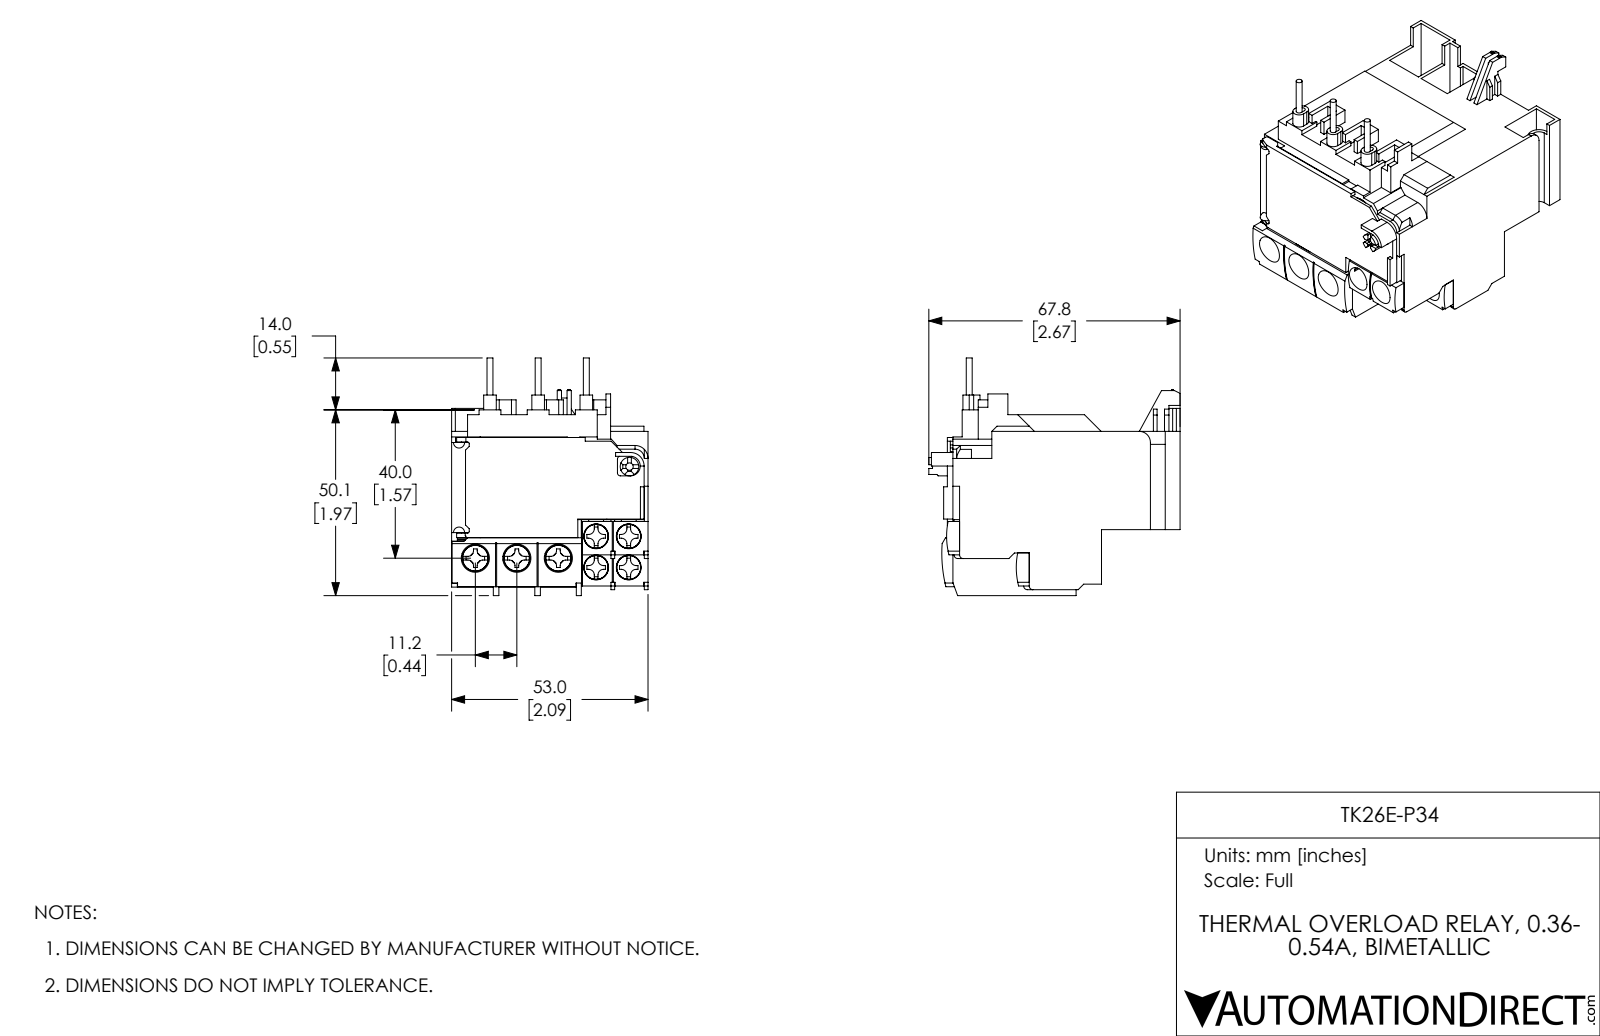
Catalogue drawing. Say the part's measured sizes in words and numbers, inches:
The part is named "TK26E-P34". Its 3-D file was written by "SolidWorks 2017 (AUTOMOTIVE_DESIGN)". It is 38 solids with 1480 faces: 1225 planar, 220 cylindrical and 35 other. Overall it measures 2.669 by 2.524 by 2.087 inches. Its volume is 6.099 cubic inches and its surface area 60.15 square inches. Round holes: 4 of diameter 0.138, 4 of diameter 0.142, 4 of diameter 0.264, 3 of diameter 0.157, 3 of diameter 0.161, 3 of diameter 0.299, 1 of diameter 0.039, 1 of diameter 0.079, 1 of diameter 0.197, 1 of diameter 0.433. Round bosses or shafts: 4 of diameter 0.26, 3 of diameter 0.063, 1 of diameter 0.236. Partial cylindrical surfaces (rounded edges, fillets, slot ends): 28 of radius 0.059, 8 of radius 0.039, 6 of radius 0.02, 6 of radius 0.067, 5 of radius 0.031, 4 of radius 0.047, 4 of radius 0.171, 3 of radius 0.189. The main face-to-face distances are 0.039, 0.354, 0.059, 0.472, 2.087, 0.079, 0.394, 0.433, 0.343, 0.028. The hole center spacings are 0.331, 0.346, 0.441, 0.479, 0.376, 0.413, 0.464, 0.74.
